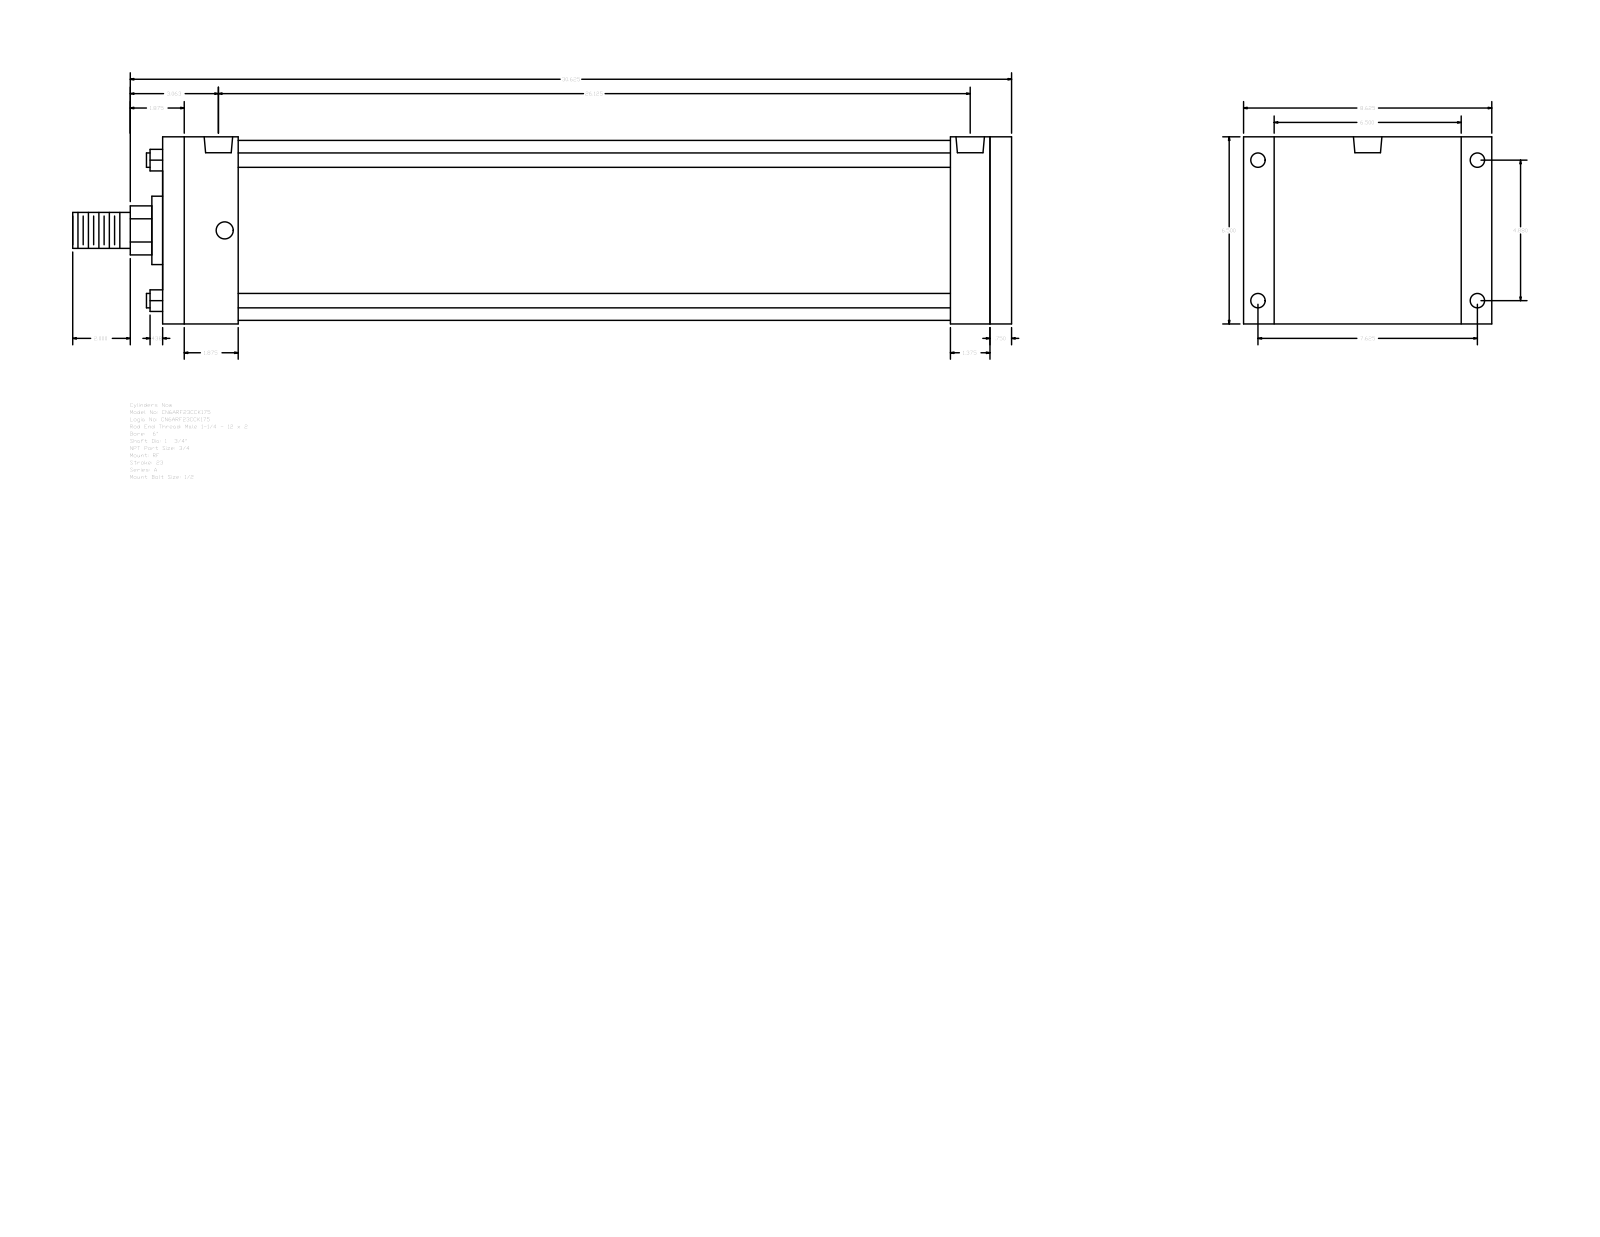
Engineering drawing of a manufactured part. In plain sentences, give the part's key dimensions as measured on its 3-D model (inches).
The part is named "A_RF__0600_1.75". Its 3-D file was written by "GSSL Pune (CONFIG_CONTROL_DESIGN)". It is 0 solids with 92 faces: 64 planar, 28 cylindrical and 0 other. Overall it measures 32.625 by 8.625 by 6.5 inches. Round holes: 4 of diameter 0.5, 4 of diameter 0.594, 2 of diameter 0.989. Round bosses or shafts: 4 of diameter 0.5, 1 of diameter 6.25, 1 of diameter 2.375, 1 of diameter 1.75, 1 of diameter 1.25. Partial cylindrical surfaces (rounded edges, fillets, slot ends): 1 of radius 0.852. The main face-to-face distances are 6.5, 29.5, 0.75, 28.75, 2.625, 26.125, 26.875, 27.375, 24.75, 1.375. The hole center spacings are 0.219, 4.88, 7.625, 9.053, 25.687, 25.906, 26.125.
